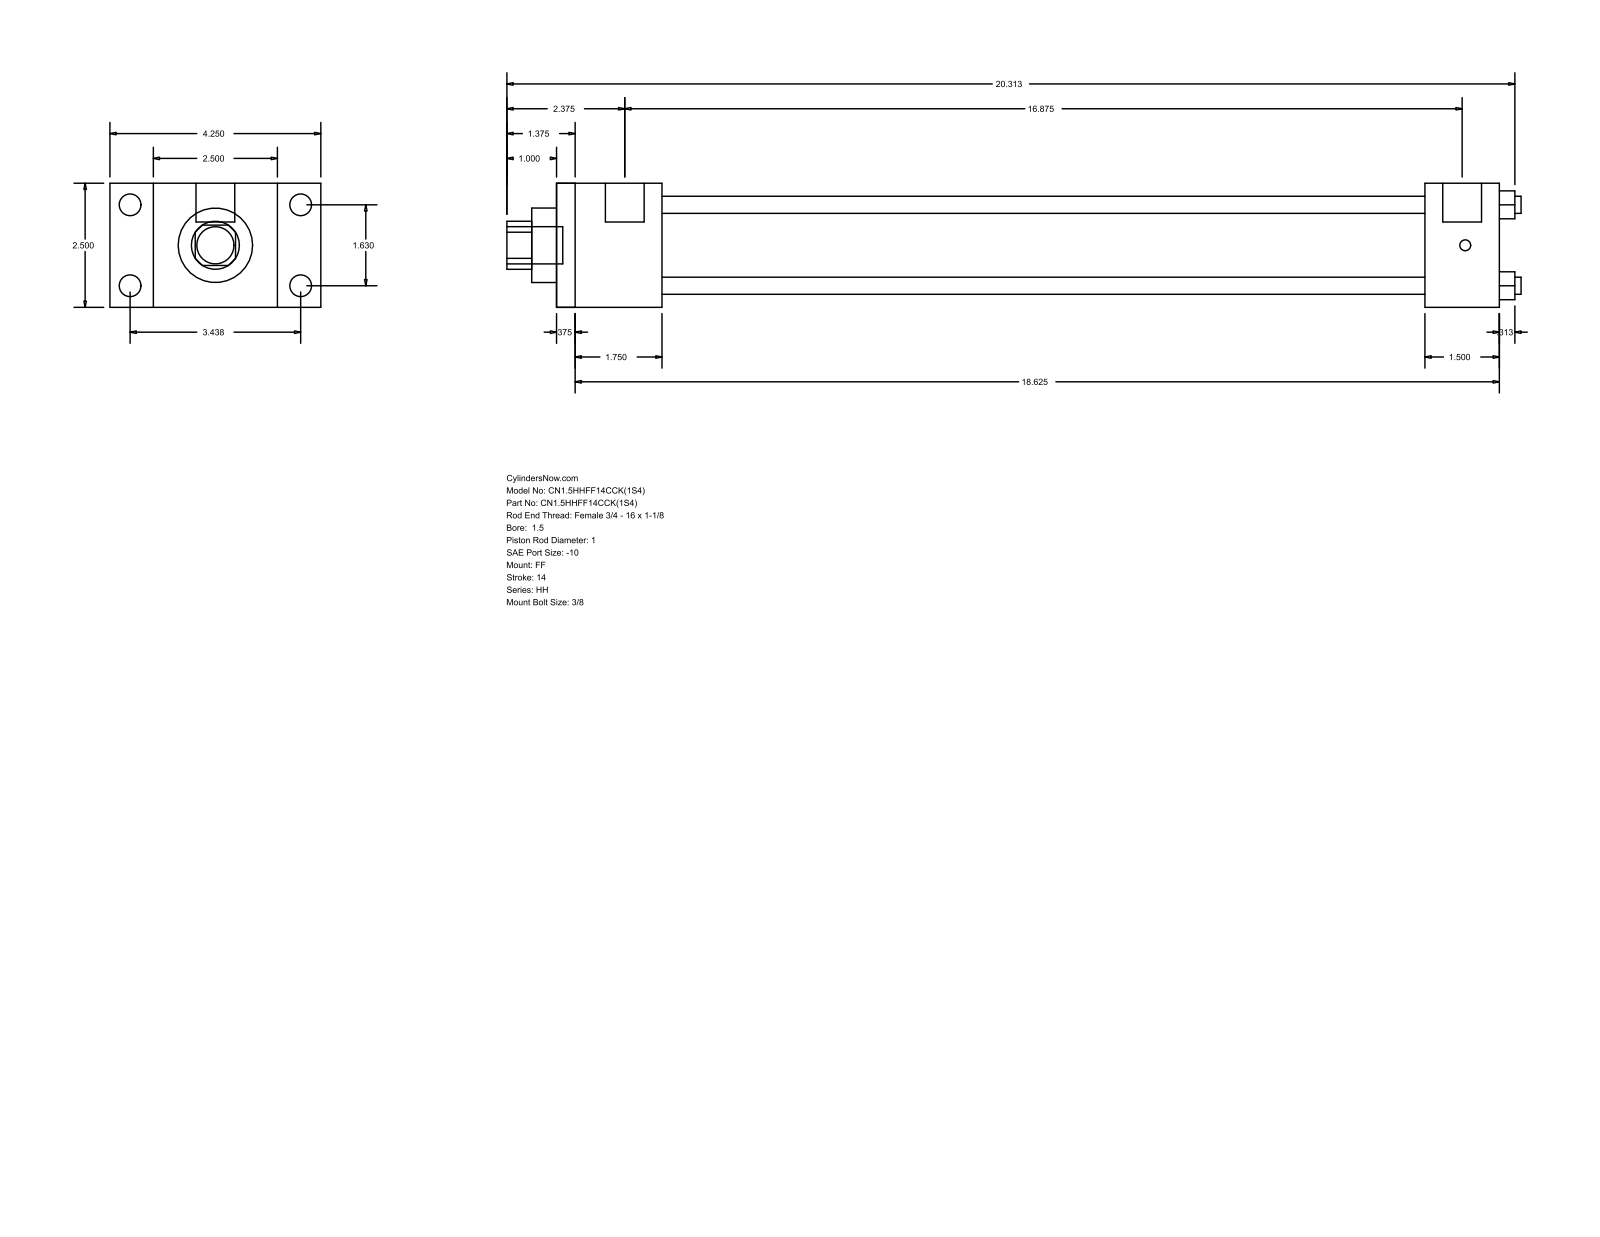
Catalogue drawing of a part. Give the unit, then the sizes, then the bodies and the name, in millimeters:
Units: millimetres
Overall size (bounding box): 519.11 × 107.95 × 63.5
Round holes (diameter × count): ⌀8.76 ×4, ⌀25.4 ×1, ⌀38.1 ×1, ⌀44.45 ×1
Round bosses / shafts (diameter × count): ⌀11.13 ×4, ⌀5.56 ×4, ⌀19.84 ×2, ⌀19.05 ×1
Partial cylindrical surfaces — rounded edges, fillets, slot ends (radius × count): R12.29 ×1
Main face-to-face distances: 63.5, 482.6, 9.52, 473.08, 53.98, 44.46, 428.62, 444.5, 434.98, 390.52
Hole centre spacings: 29.27, 41.4, 58.55
Bodies: 0 solids, 92 faces (64 planar, 28 cylindrical, 0 other)
Part name (STEP PRODUCT): HH_FF__0150_1
STEP written by: GSSL Pune (CONFIG_CONTROL_DESIGN)
